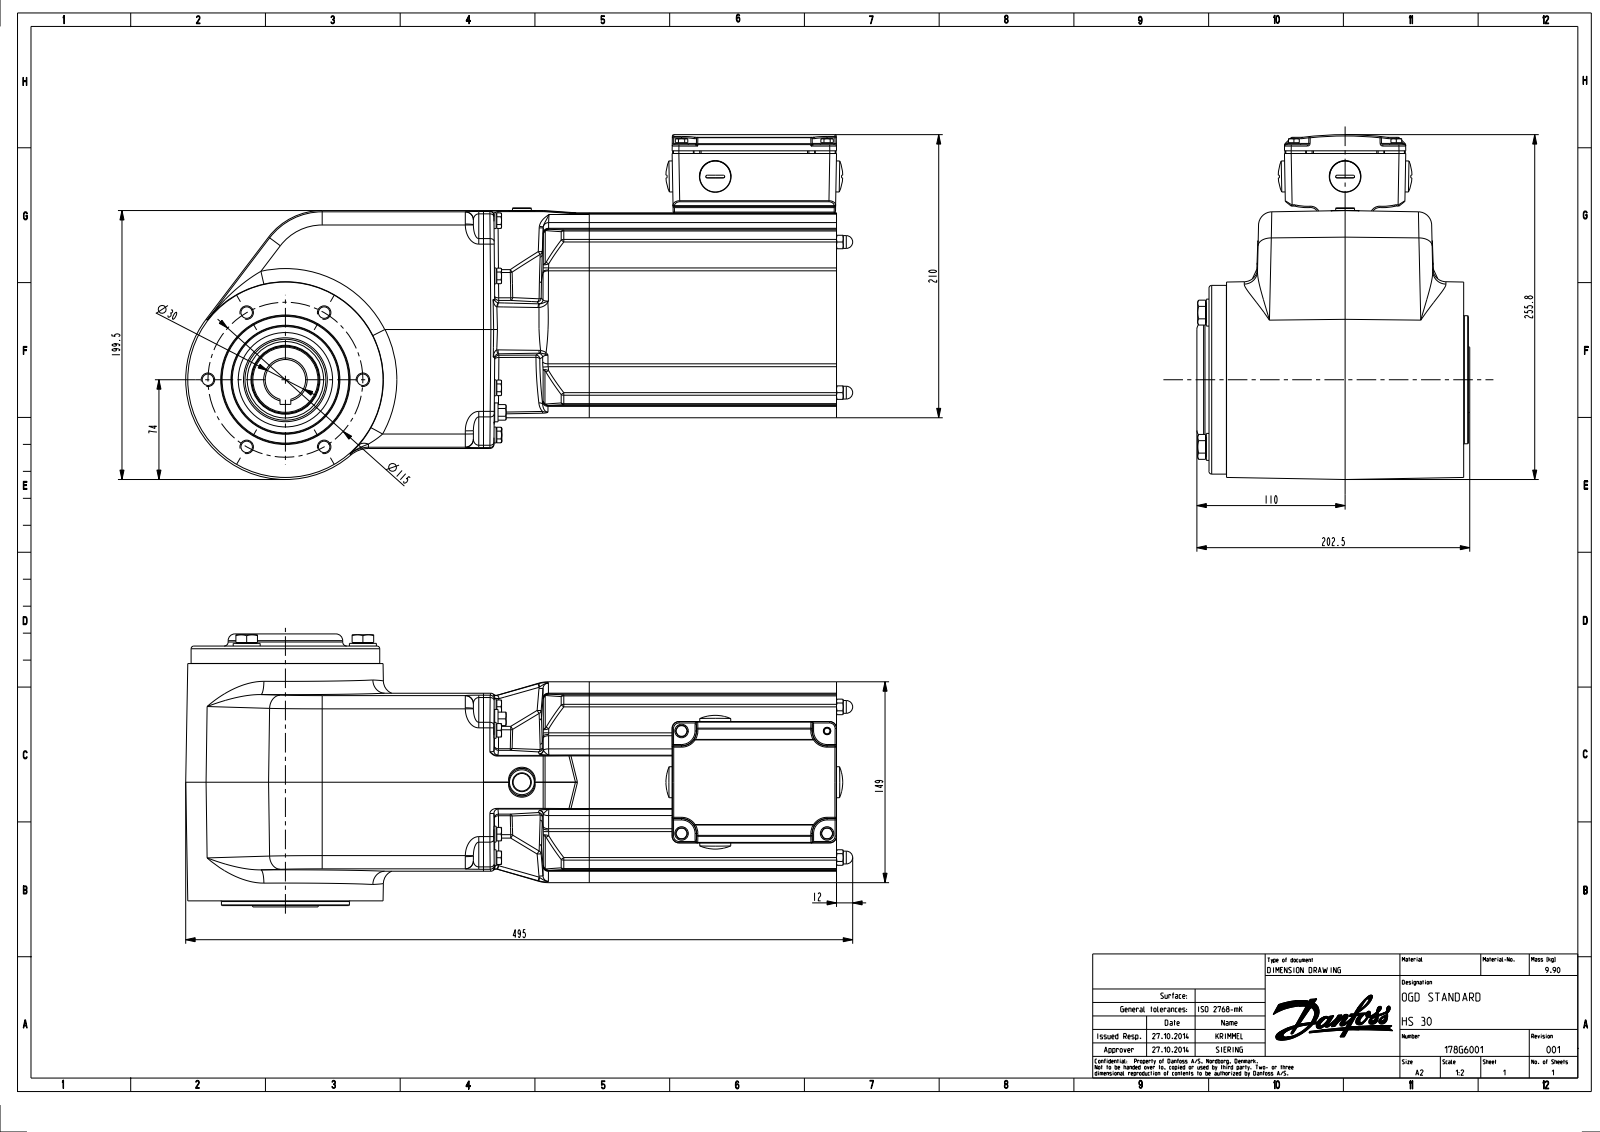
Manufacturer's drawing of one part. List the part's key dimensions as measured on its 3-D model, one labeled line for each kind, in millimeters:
Part name (STEP PRODUCT): 178G6001_HUELLE_SW001
STEP written by: PRO/ENGINEER BY PARAMETRIC TECHNOLOGY CORPORATION, 2013230 (AUTOMOTIVE_DESIGN)
Units: millimetres
Bodies: 1 solid, 1304 faces (353 planar, 330 cylindrical, 621 other)
Overall size (bounding box): 495 × 255.8 × 202.5
Volume: 10 870 000 mm³ · Surface area: 415 371 mm²
Round holes (diameter × count): ⌀6.1 ×8, ⌀8.5 ×6, ⌀30 ×1, ⌀30.5 ×1, ⌀31.4 ×1, ⌀49 ×1, ⌀70 ×1, ⌀80 ×1
Round bosses / shafts (diameter × count): ⌀11.8 ×8, ⌀9 ×8, ⌀6 ×8, ⌀23 ×4, ⌀10 ×4, ⌀9.5 ×4, ⌀7 ×4, ⌀20 ×3
Partial cylindrical surfaces — rounded edges, fillets, slot ends (radius × count): R1 ×46, R3 ×36, R5 ×26, R6 ×14, R10 ×14, R0.5 ×8, R4 ×4, R4 ×4
Main face-to-face distances: 133.38, 176.5, 189, 9, 4.5, 198, 133.39, 3.5, 201.5, 192.5
Hole centre spacings: 57.5, 99.59, 44.58, 77, 103.01, 119.29, 151.18, 99.6
